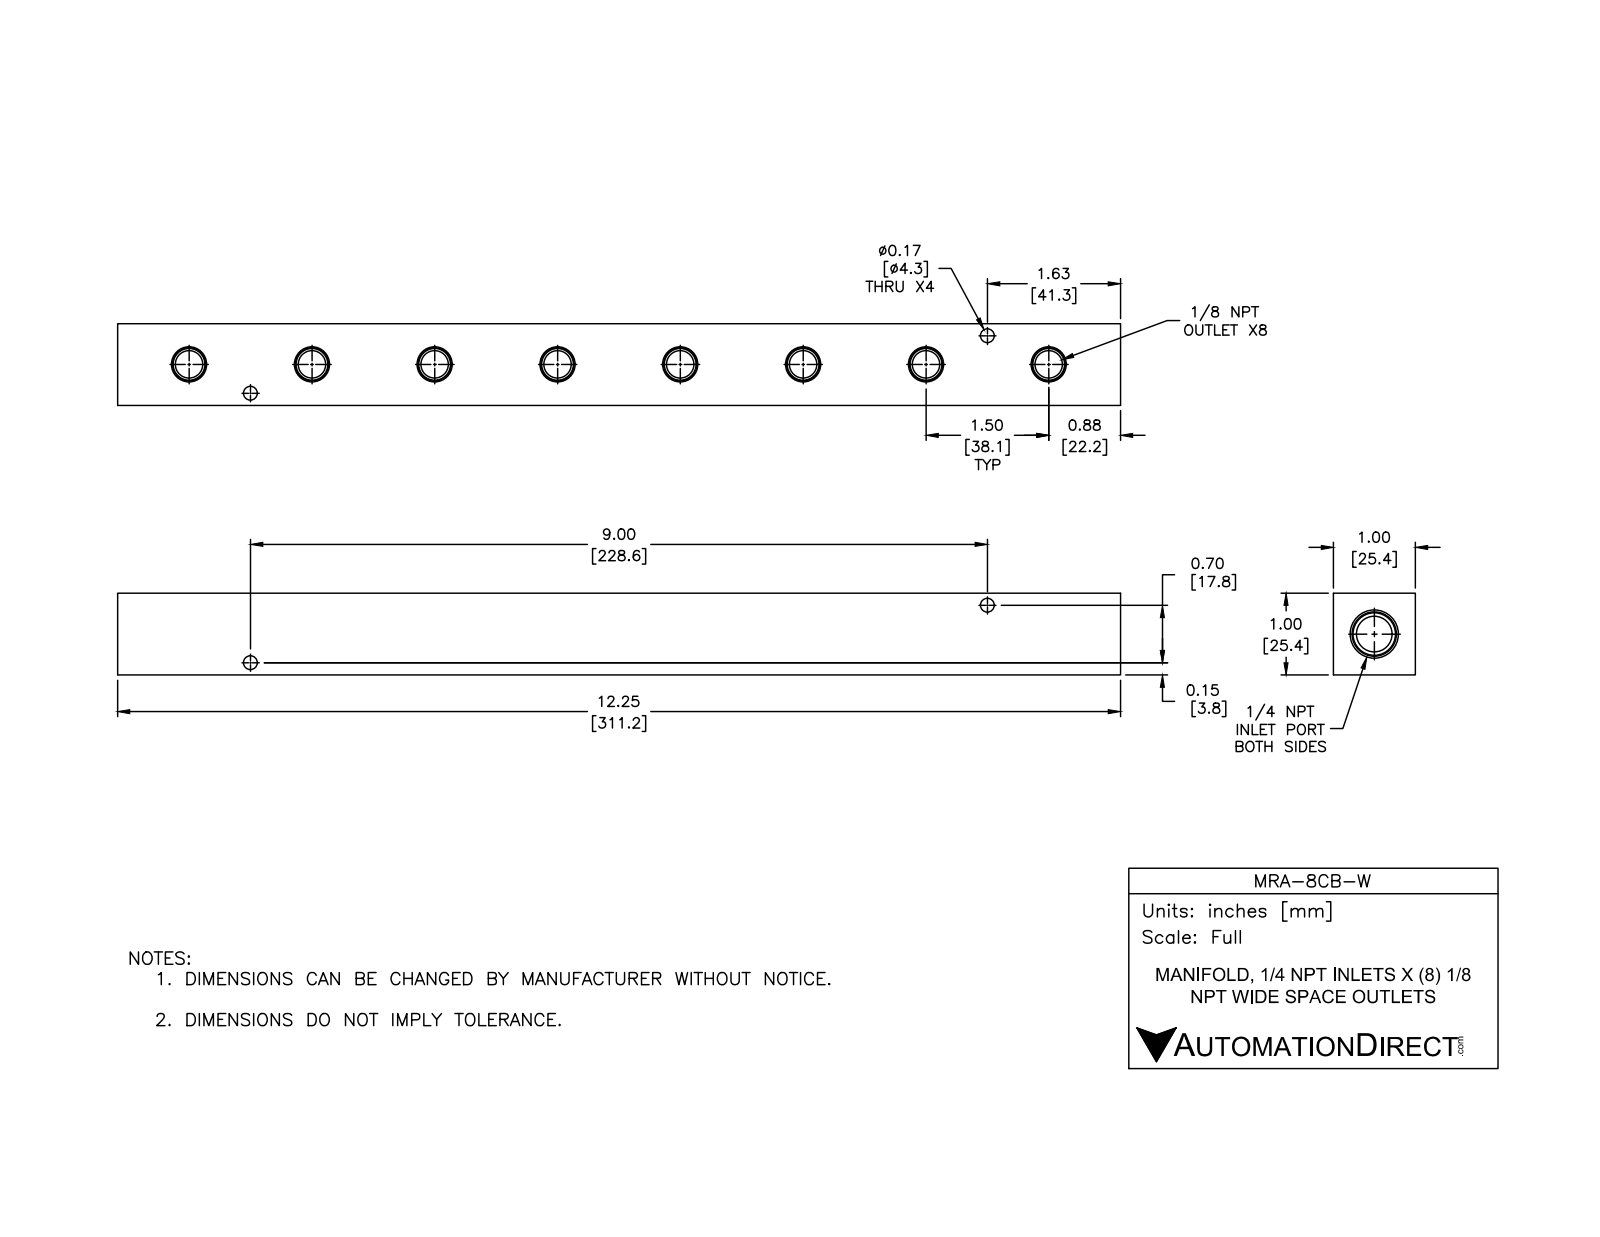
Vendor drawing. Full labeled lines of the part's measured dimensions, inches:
Part name (STEP PRODUCT): MRA-8CB-W
STEP written by: SolidWorks 2015 (CONFIG_CONTROL_DESIGN)
Units: inches
Bodies: 1 solid, 90 faces (16 planar, 34 cylindrical, 40 other)
Overall size (bounding box): 12.25 × 1 × 1
Volume: 9.976 in³ · Surface area: 70.91 in²
Round holes (diameter × count): ⌀0.332 ×8, ⌀0.17 ×4, ⌀0.438 ×1
Main face-to-face distances: 1, 12.25, 0.73, 0.27, 0.39, 11.86, 11.47
Hole centre spacings: 1.5, 3, 4.5, 0.828, 6, 7.5, 2.277, 3.766
